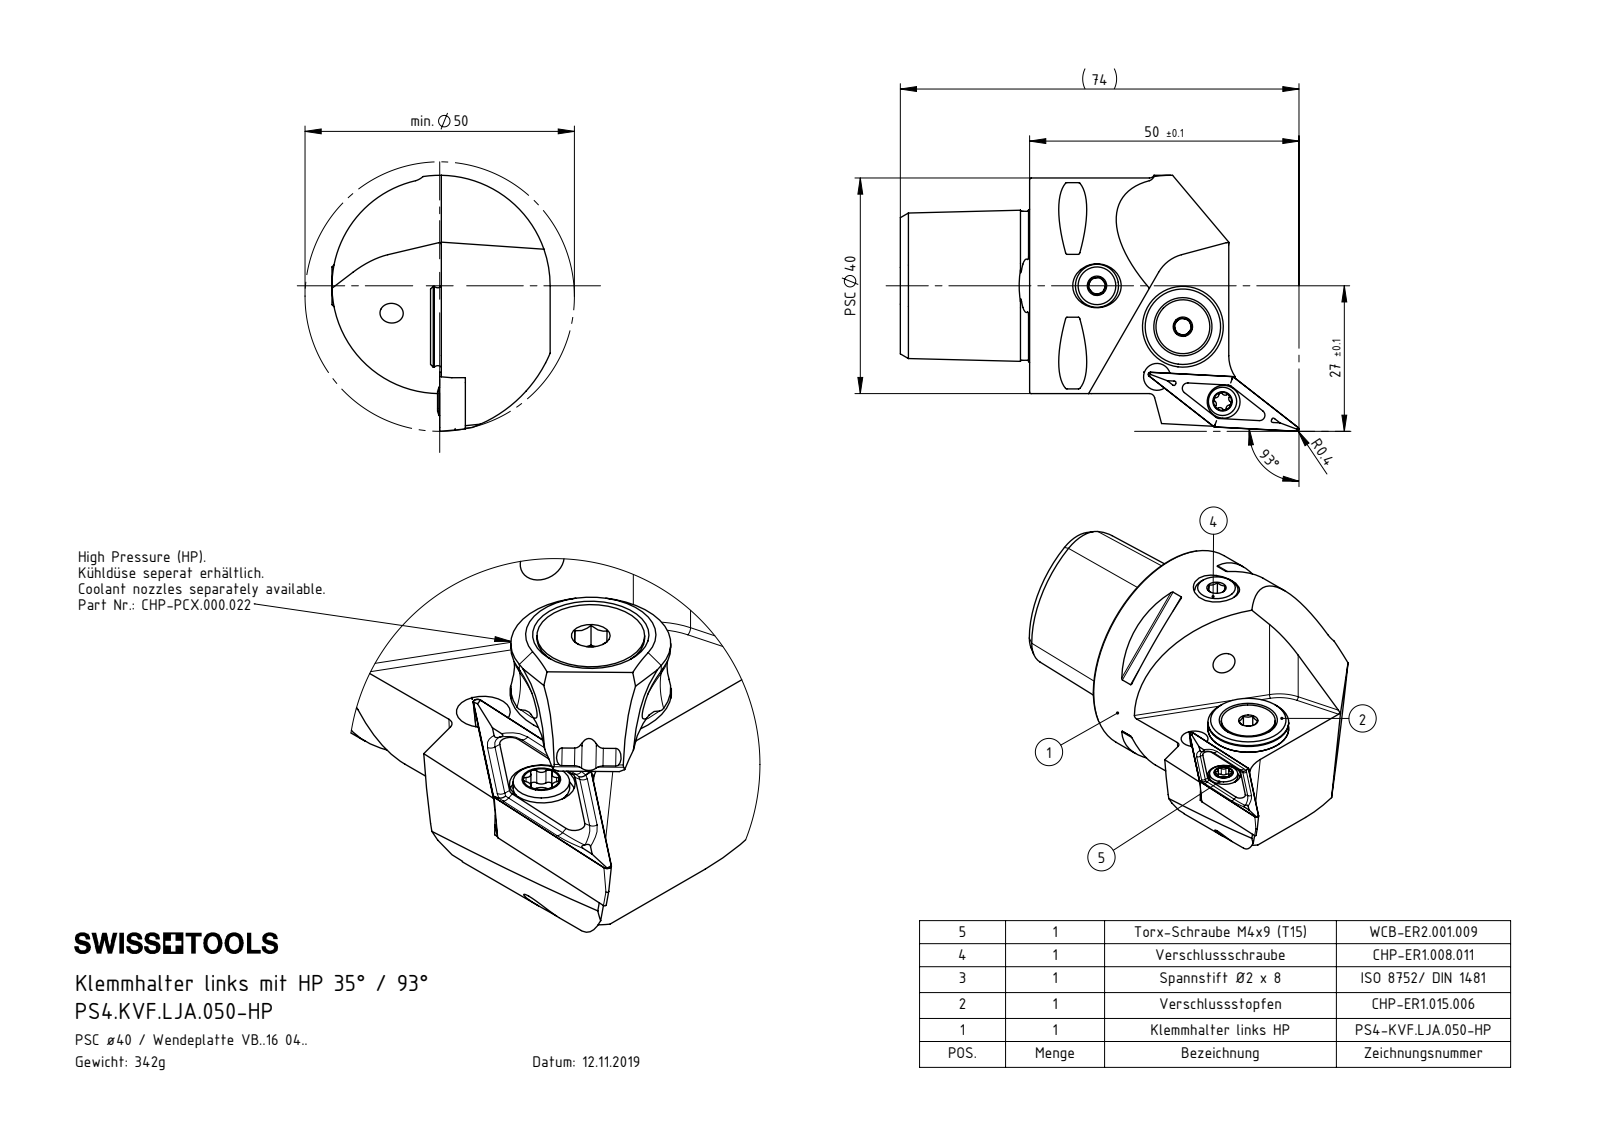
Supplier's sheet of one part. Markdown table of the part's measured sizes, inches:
| quantity | value |
| --- | --- |
| part name | VBMT160404; DIN 3771 - 13x1; PS4.KVF.LJA.050-HP; PS4-KVF.LJA.050-HP_A (+6 more) |
| STEP written by | SolidWorks 2017 (AUTOMOTIVE_DESIGN) |
| units | inches |
| bodies | 8 solids, 281 faces (93 planar, 64 cylindrical, 124 other) |
| overall size | 2.913 × 1.87 × 1.594 |
| volume | 2.652 in³ |
| surface area | 23.08 in² |
| round holes (diameter × count) | 0.13 × 2, 0.165 × 2, 0.197 × 2, 0.047 × 1, 0.079 × 1, 0.098 × 1, 0.118 × 1, 0.157 × 1, 0.173 × 1, 0.181 × 1, 0.205 × 1, 0.24 × 1 |
| round bosses / shafts (diameter × count) | 1.575 × 1, 0.591 × 1, 0.528 × 1, 0.394 × 1, 0.315 × 1, 0.217 × 1, 0.207 × 1, 0.197 × 1 |
| partial cylindrical surfaces (radius × count) | 0.012 × 8, 0.013 × 6, 0.023 × 6, 0.006 × 2, 0.02 × 2, 0.276 × 2, 0.118 × 1, 0.807 × 1 |
| main face-to-face distances | 0.177, 0.176, 0.945, 0.618, 0.62, 0.795, 0.611, 0.591, 1.39, 0.354 |
| hole center spacings | 0.02, 0.177, 0.412, 0.502, 0.511, 0.52, 0.536, 0.541 |
